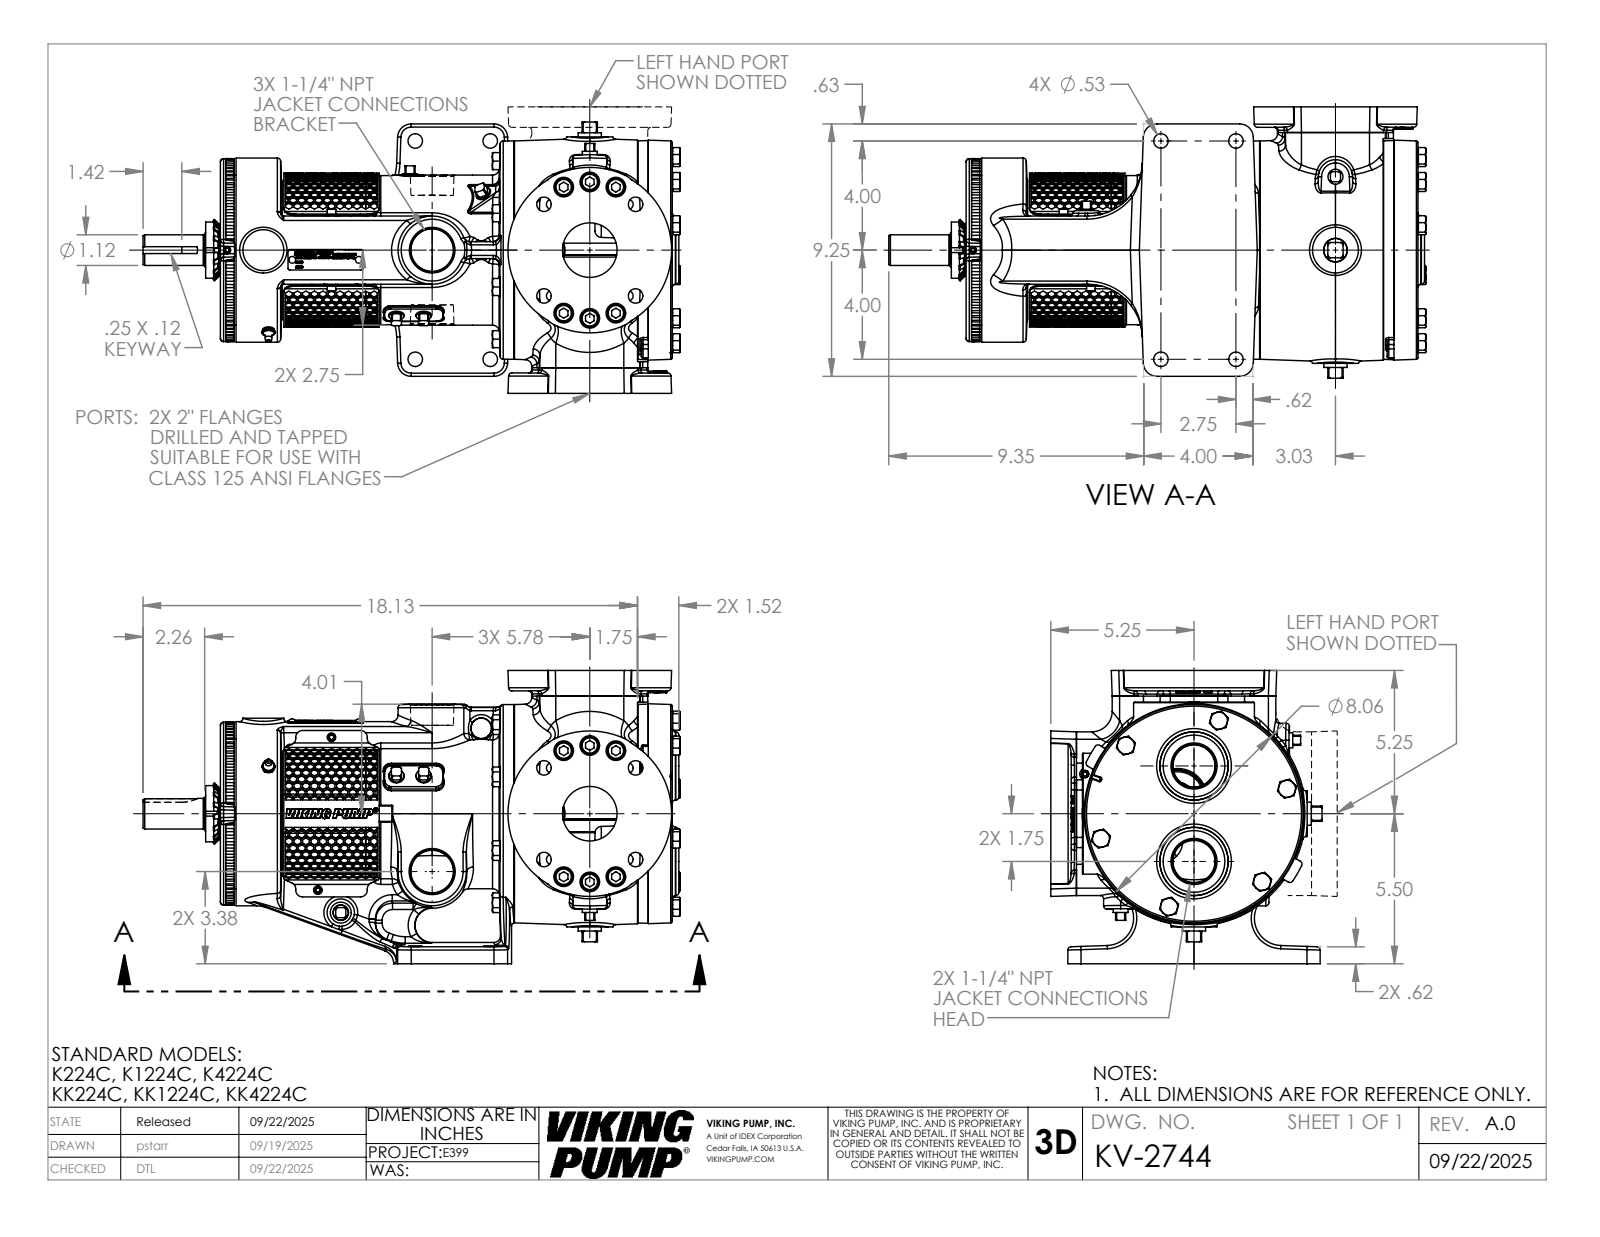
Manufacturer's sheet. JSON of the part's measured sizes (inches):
{"part_name": "KV-2744", "step_written_by": "SolidWorks 2024 (AUTOMOTIVE_DESIGN)", "units": "inches", "bodies": {"solids": 1, "faces": 4731, "planar": 1496, "cylindrical": 655, "other": 2580}, "overall_size": [19.695, 10.75, 9.945], "volume_in3": 659.4, "surface_area_in2": 1041, "round_holes": [[0.531, 12], [0.719, 12], [0.25, 9], [0.368, 8], [0.78, 8], [0.197, 6], [0.159, 2], [0.313, 2], [2, 2], [0.257, 1], [0.453, 1], [1.387, 1]], "round_bosses_or_shafts": [[0.625, 23], [0.625, 3], [0.312, 3], [0.19, 3], [8, 1], [6.75, 1], [5.5, 1], [5.497, 1]], "partial_cylinders_radius": [[0.01, 96], [0.12, 42], [0.24, 22], [0.03, 20], [1, 18], [0.12, 16], [0.06, 9], [0.25, 8]], "face_to_face_distances": [10.75, 4, 11.245, 5.324, 16.569, 0.5, 16.069, 0.574, 4.75, 15.995], "hole_center_spacings": [3, 1.03, 2.5, 0.273, 0.976, 1.376, 2.187, 2.385]}
